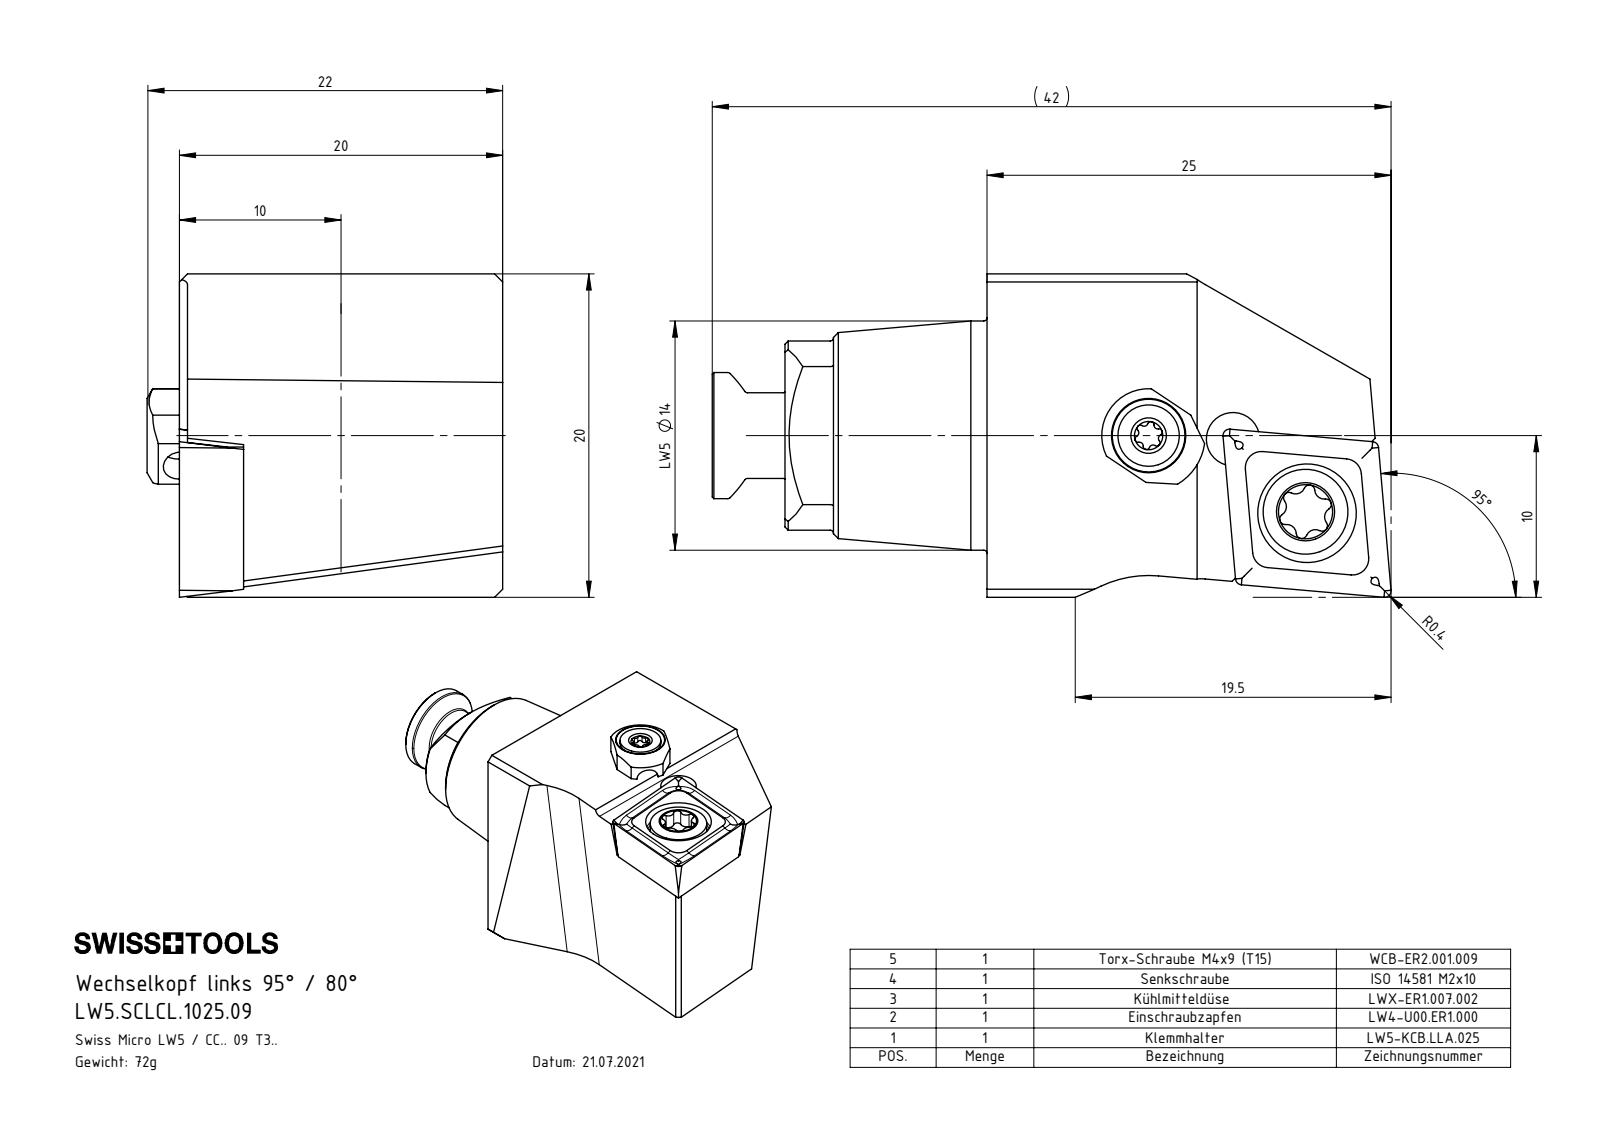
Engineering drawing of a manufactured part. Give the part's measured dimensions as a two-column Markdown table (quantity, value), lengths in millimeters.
| quantity | value |
| --- | --- |
| part name | ISO 14581 - M2x10; LWX-ER1.007.002; WCB-ER2.001.009_A; LW5-KCB.LLA.025_A (+3 more) |
| STEP written by | SolidWorks 2022 (CONFIG_CONTROL_DESIGN) |
| units | millimeters |
| bodies | 6 solids, 262 faces (69 planar, 80 cylindrical, 113 other) |
| overall size | 42 × 22 × 20 |
| volume | 9 141 mm³ |
| surface area | 4 421 mm² |
| round holes (diameter × count) | 3 × 2, 3.3 × 2, 1.6 × 1, 2 × 1, 2.5 × 1, 4.4 × 1, 5.5 × 1, 6.1 × 1 |
| round bosses / shafts (diameter × count) | 14.17 × 1, 7.7 × 1, 6 × 1, 5.3 × 1, 5.25 × 1, 5 × 1, 4 × 1, 3.8 × 1 |
| partial cylindrical surfaces (radius × count) | 0.2 × 8, 0.24 × 6, 0.34 × 6, 0.59 × 6, 0.5 × 1, 1 × 1, 2.9 × 1, 3.5 × 1 |
| main face-to-face distances | 20, 16.03, 3.97, 19.5, 3.47, 0.5, 7.5, 2, 3, 12.5 |
| hole center spacings | 5.22, 6.35, 6.48, 10.79, 10.91 |
